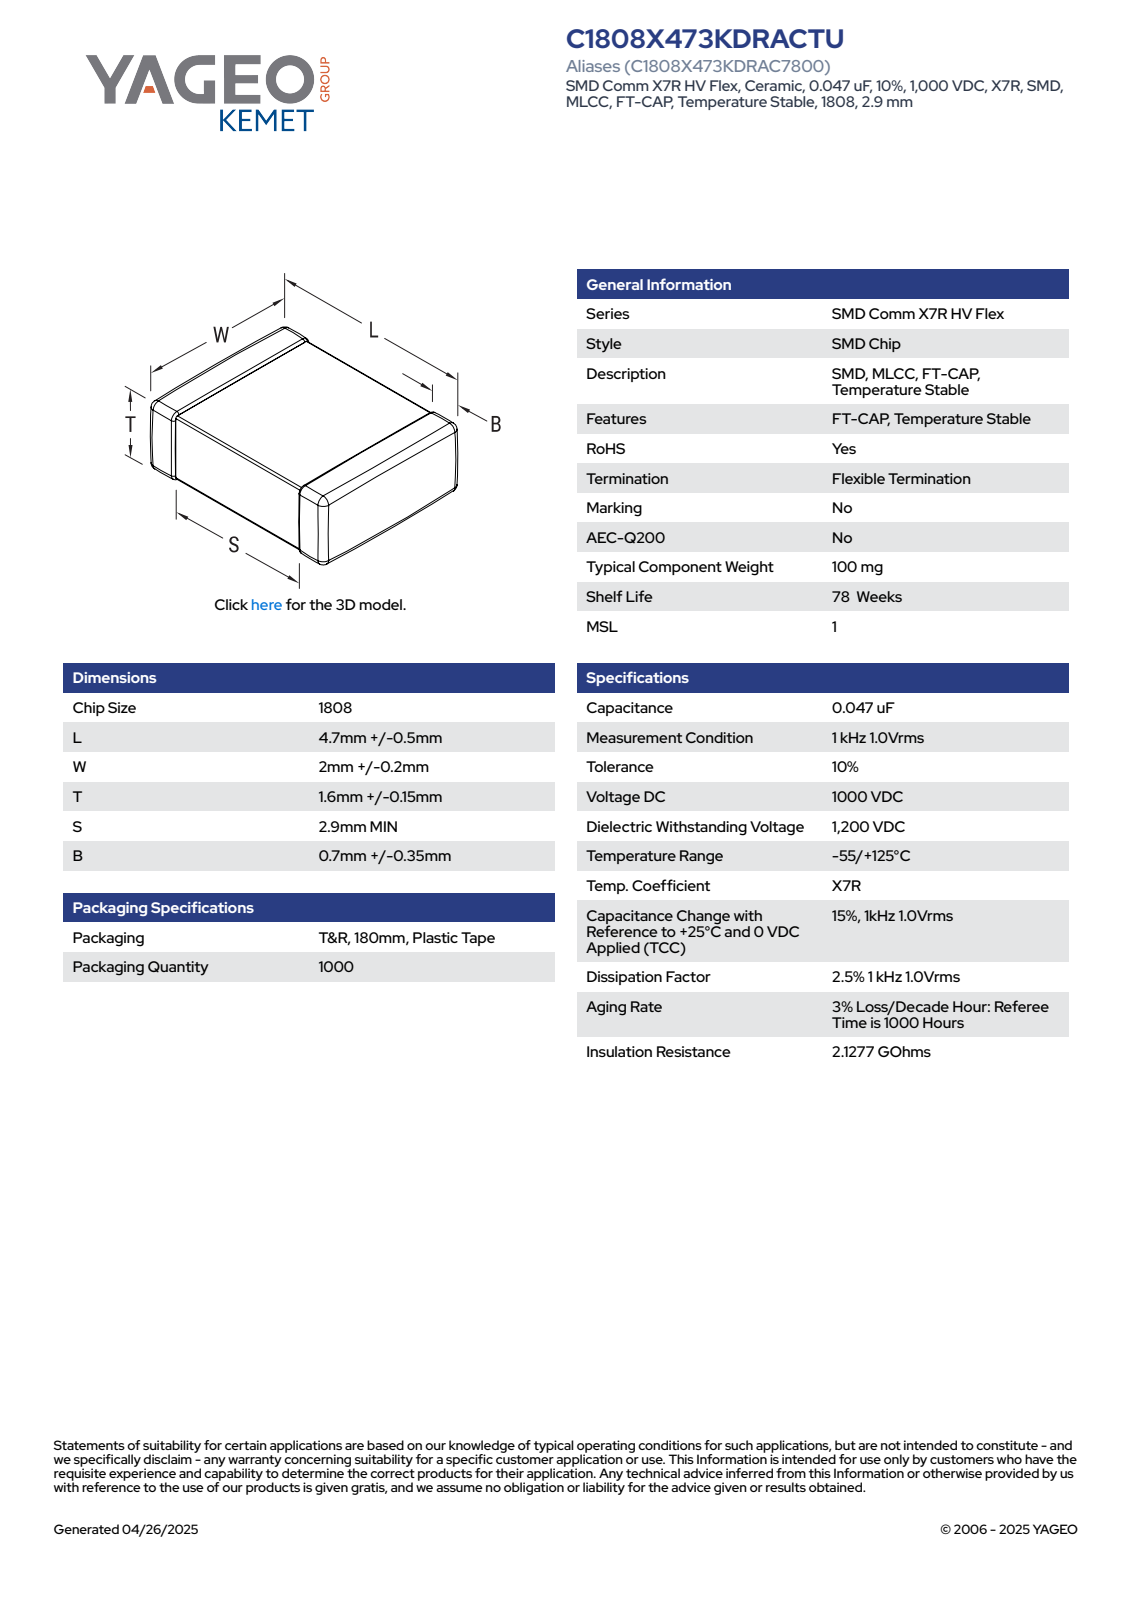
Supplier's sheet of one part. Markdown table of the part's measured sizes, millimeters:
| quantity | value |
| --- | --- |
| part name | CCS_CCSTD_1808_L5.2W2.2T1.75B0.7 |
| STEP written by | SolidWorks 2021 (AUTOMOTIVE_DESIGN) |
| units | millimeters |
| bodies | 4 solids, 125 faces (71 planar, 38 cylindrical, 16 other) |
| overall size | 5.2 × 2.2 × 1.75 |
| volume | 19 mm³ |
| surface area | 48 mm² |
| main face-to-face distances | 1.7, 2.15, 1.65, 2.1, 1.75, 5.2, 2.2, 1.71, 1.66, 0.33 |
